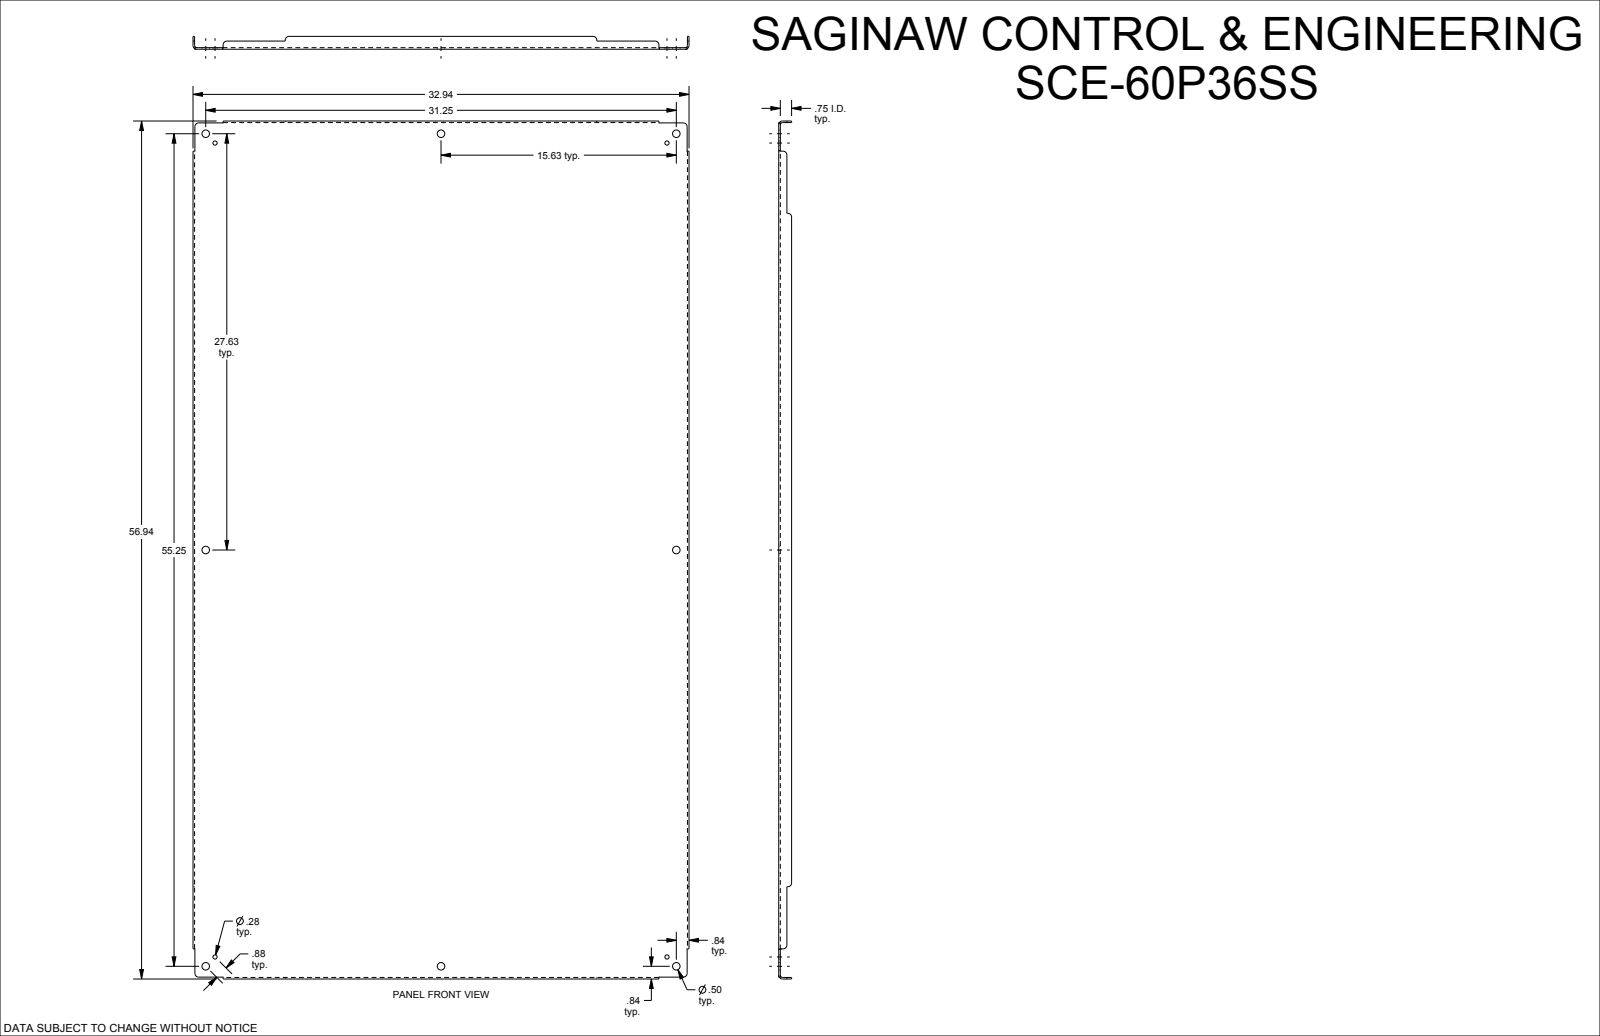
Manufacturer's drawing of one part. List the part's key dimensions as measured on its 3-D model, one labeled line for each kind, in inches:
Part name (STEP PRODUCT): SCE-60P36SS
STEP written by: SolidWorks 2019 (CONFIG_CONTROL_DESIGN)
Units: inches
Bodies: 1 solid, 110 faces (46 planar, 40 cylindrical, 24 other)
Overall size (bounding box): 56.938 × 32.938 × 0.854
Volume: 204.9 in³ · Surface area: 3 961 in²
Round holes (diameter × count): ⌀0.5 ×8, ⌀0.281 ×4
Partial cylindrical surfaces — rounded edges, fillets, slot ends (radius × count): R0.25 ×12, R0.246 ×4, R0.142 ×2, R0.143 ×2
Main face-to-face distances: 0.104, 0.104, 32.833, 56.833, 32.938, 32.729, 56.938, 56.729, 0.75, 0.854
Hole centre spacings: 0.875, 15.019, 15.625, 27.013, 27.625, 30.638, 31.738, 40.837
